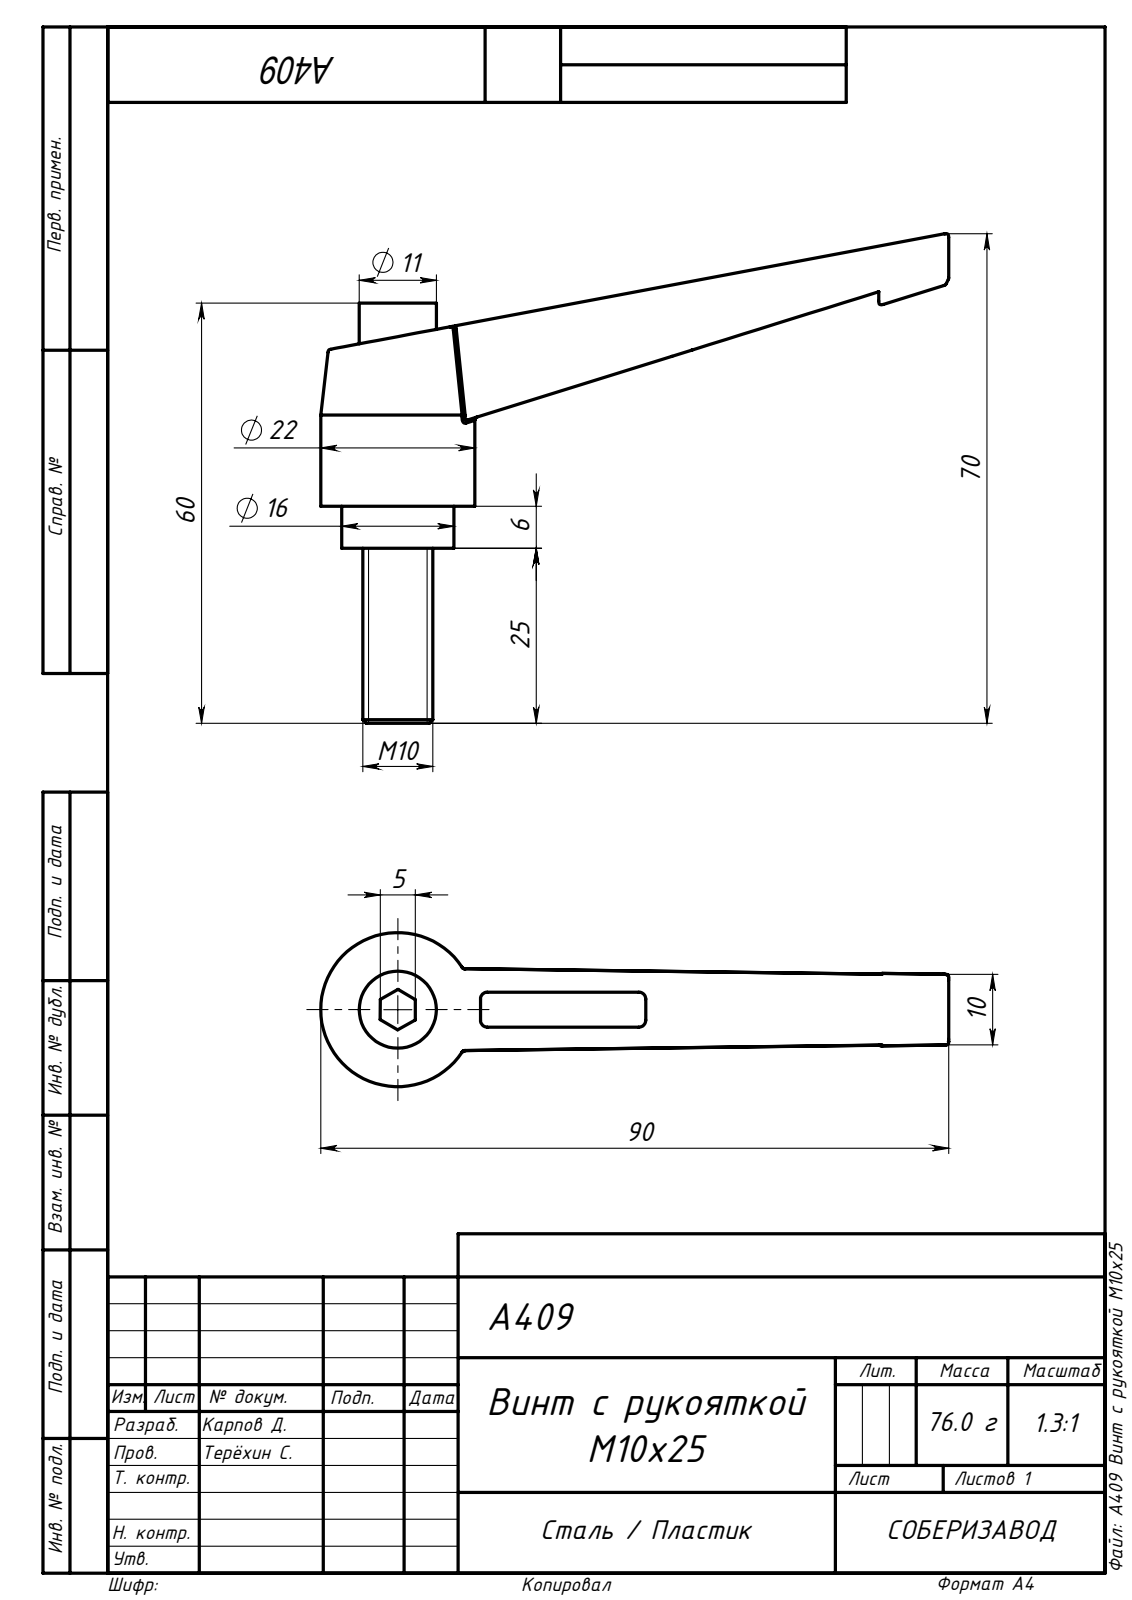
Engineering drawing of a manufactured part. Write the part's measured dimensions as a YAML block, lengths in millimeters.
part_name: "A409 Винт с рукояткой М10х25"
step_written_by: "SolidWorks 2020 (AUTOMOTIVE_DESIGN)"
units: millimeters
bodies: {solids: 1, faces: 81, planar: 31, cylindrical: 12, other: 38}
overall_size: [89.62, 69.91, 22]
volume: 16277
surface_area: 7051
round_bosses_or_shafts:
  - {diameter: 22, count: 1}
  - {diameter: 16, count: 1}
  - {diameter: 11, count: 1}
  - {diameter: 10, count: 1}
partial_cylinders:
  - {radius: 1, count: 4}
face_to_face_distances: [6, 6.93, 35, 29, 25, 31, 60, 60.48, 5, 57]
